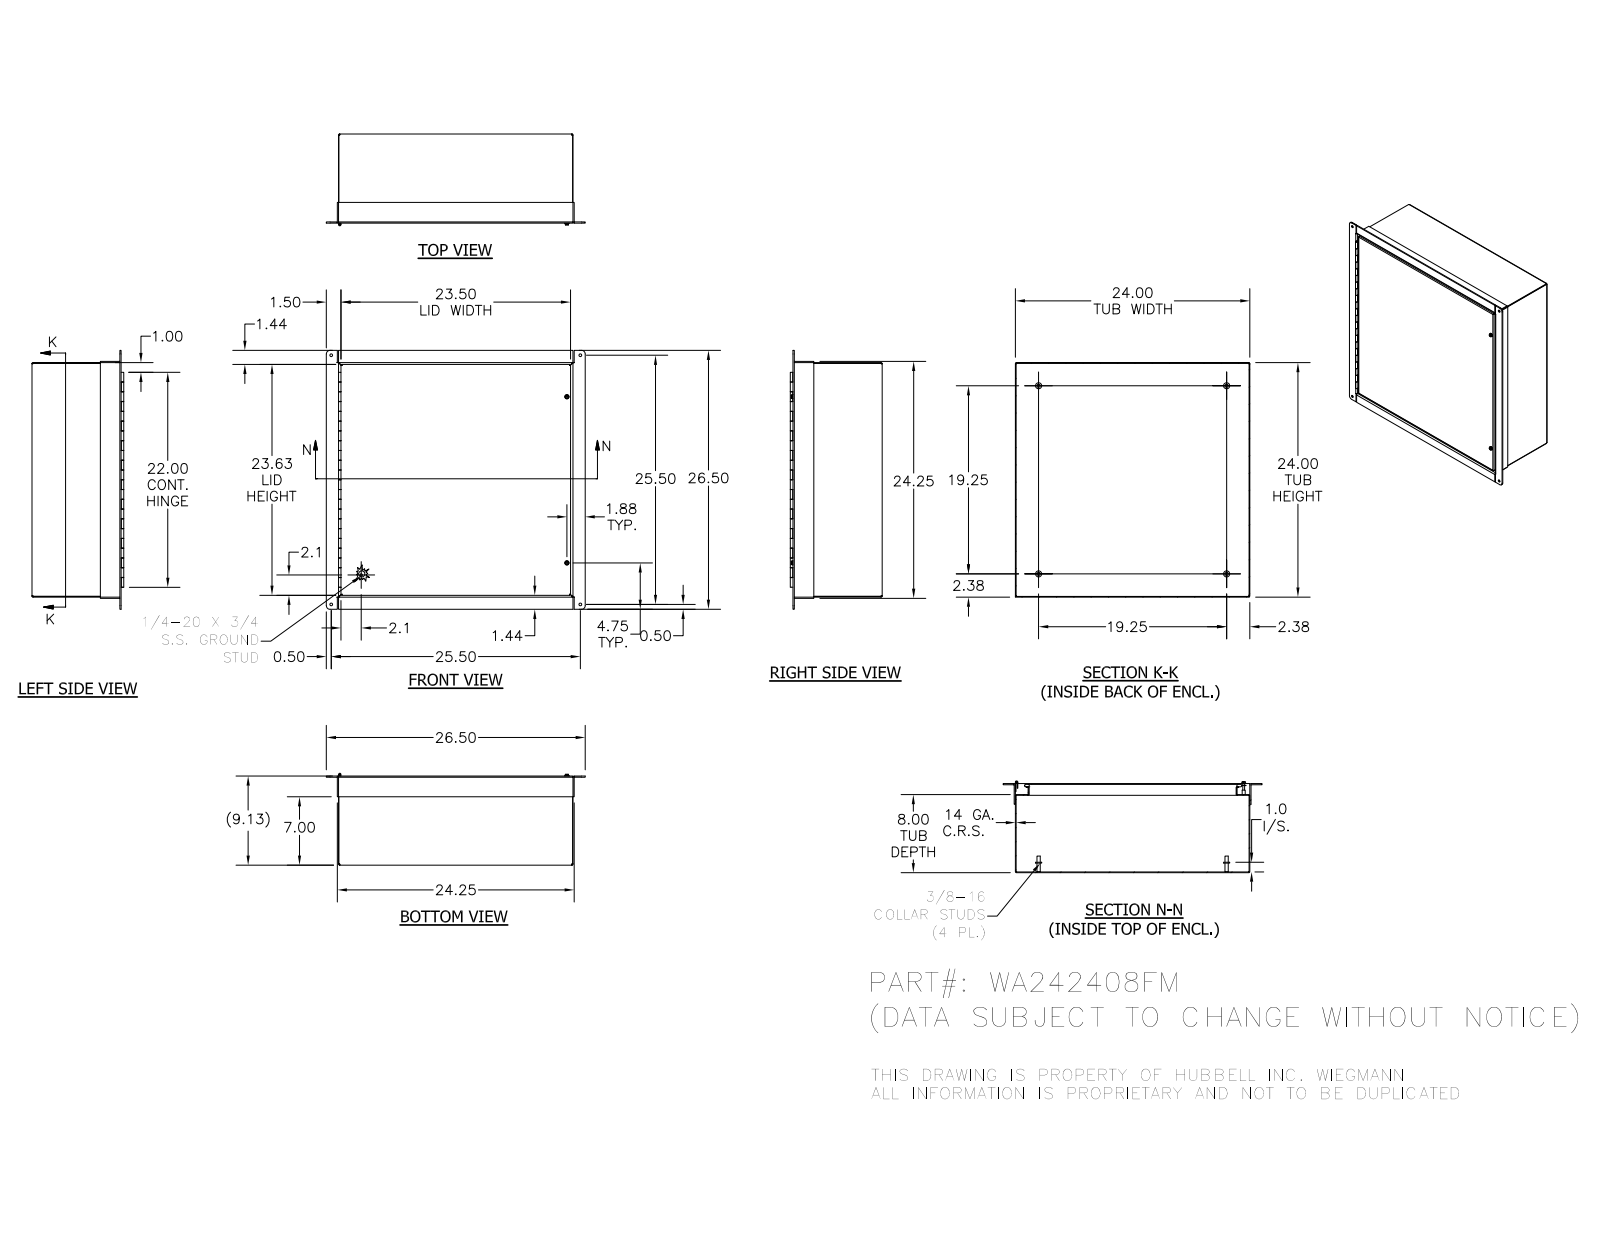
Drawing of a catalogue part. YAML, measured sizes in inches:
part_name: "WA242408FMBKP; WA2424FMLID; 388116; H6010101T (+8 more)"
step_written_by: "Autodesk Inventor 2016 (AUTOMOTIVE_DESIGN)"
units: inches
bodies: {solids: 23, faces: 633, planar: 395, cylindrical: 167, other: 71}
overall_size: [26.5, 26.5, 9.4]
volume: 211.3
surface_area: 5191
round_holes:
  - {diameter: 0.281, count: 6}
  - {diameter: 0.375, count: 4}
  - {diameter: 0.156, count: 2}
  - {diameter: 0.188, count: 2}
  - {diameter: 0.278, count: 2}
  - {diameter: 0.125, count: 1}
round_bosses_or_shafts:
  - {diameter: 0.625, count: 4}
  - {diameter: 0.33, count: 4}
  - {diameter: 0.453, count: 2}
  - {diameter: 0.437, count: 2}
  - {diameter: 0.414, count: 2}
  - {diameter: 0.313, count: 2}
  - {diameter: 0.25, count: 2}
  - {diameter: 0.19, count: 2}
partial_cylinders:
  - {radius: 0.031, count: 24}
  - {radius: 0.105, count: 20}
  - {radius: 0.07, count: 8}
  - {radius: 0.125, count: 8}
  - {radius: 0.156, count: 4}
  - {radius: 0.375, count: 4}
  - {radius: 0.089, count: 2}
face_to_face_distances: [0.074, 9.041, 23.926, 8.967, 9.115, 24, 23.852, 0.125, 7.926, 1.115]
hole_center_spacings: [4.467, 17, 21.294, 25.5, 7, 14, 24.496, 24.497]
